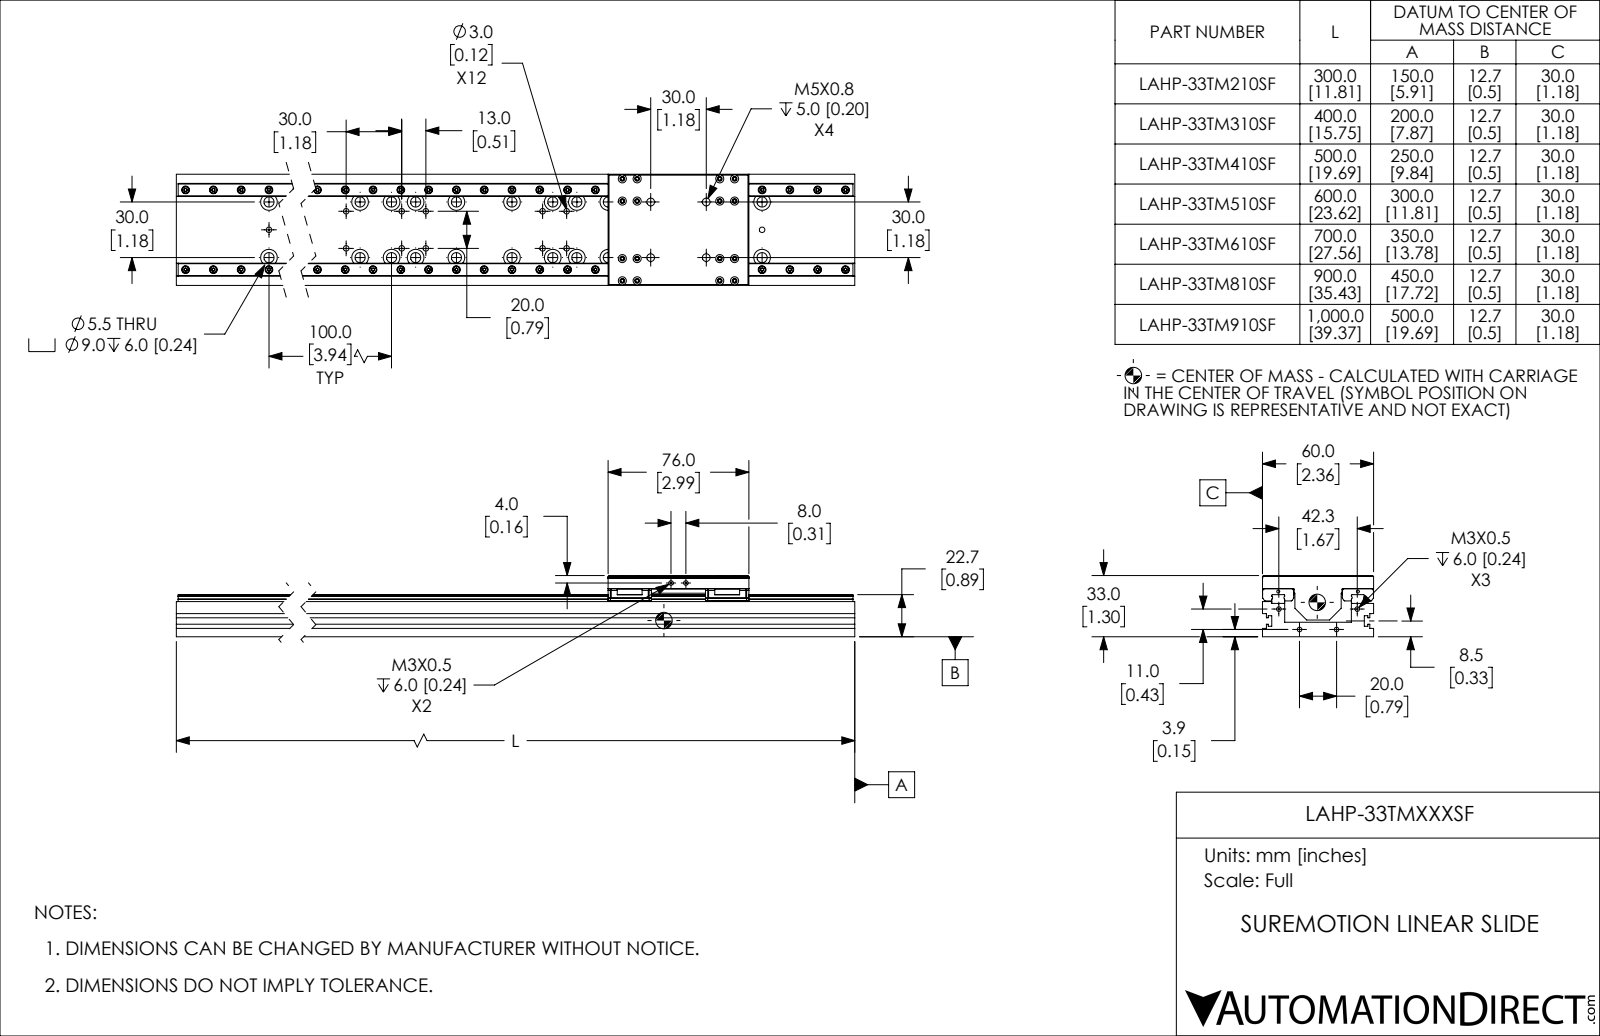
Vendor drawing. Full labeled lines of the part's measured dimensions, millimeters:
Part name (STEP PRODUCT): LAHP-33TM810SF; LAHP-33TM810SF_CARRIAGE; LAHP-33TM810SF_BASE
STEP written by: SolidWorks 2019 (CONFIG_CONTROL_DESIGN)
Units: millimetres
Bodies: 2 solids, 5338 faces (2471 planar, 1579 cylindrical, 1288 other)
Overall size (bounding box): 900 × 60 × 33
Volume: 696 300 mm³ · Surface area: 248 700 mm²
Round holes (diameter × count): ⌀4.2 ×124, ⌀1.6 ×122, ⌀2.4 ×120, ⌀5.5 ×30, ⌀9 ×30, ⌀1.6 ×16, ⌀2.6 ×16, ⌀4.4 ×16, ⌀3 ×14, ⌀2.5 ×6, ⌀3.3 ×1
Round bosses / shafts (diameter × count): ⌀3.8 ×120, ⌀2 ×120
Partial cylindrical surfaces — rounded edges, fillets, slot ends (radius × count): R0.2 ×8, R0.5 ×8, R0.9 ×4, R0.3 ×2, R7.3 ×1
Main face-to-face distances: 7.8, 12, 48, 7, 5, 43, 55, 22.7, 14.9, 36
Hole centre spacings: 30, 100, 104.4, 200, 202.2, 300, 301.5, 400
